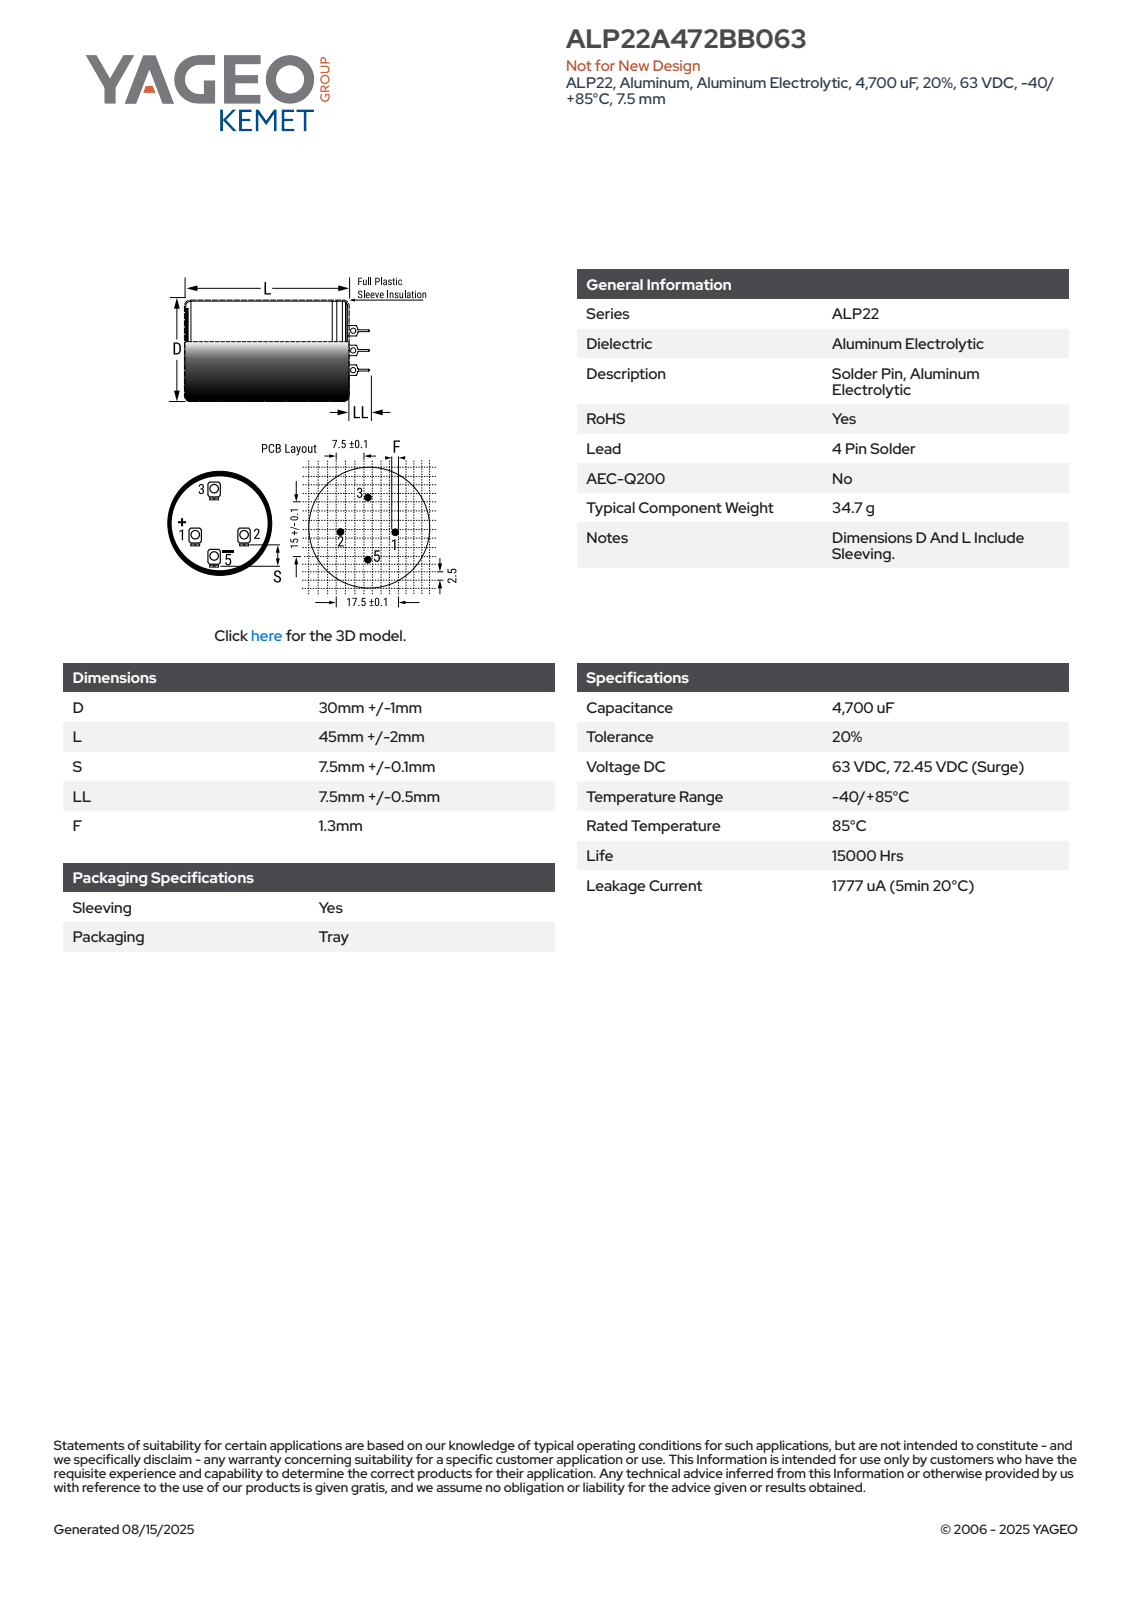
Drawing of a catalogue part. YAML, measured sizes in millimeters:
part_name: "CARS4_D31L47LL7.5S7.5F1.3; Terminal_SolderTag7.5; Terminal_Rivet; Can4_3"
step_written_by: "SolidWorks 2014 (AUTOMOTIVE_DESIGN)"
units: millimeters
bodies: {solids: 9, faces: 230, planar: 113, cylindrical: 59, other: 58}
overall_size: [54.5, 31, 31]
volume: 35253
surface_area: 6376
round_holes:
  - {diameter: 1.3, count: 4}
  - {diameter: 1, count: 3}
round_bosses_or_shafts:
  - {diameter: 3, count: 4}
  - {diameter: 31, count: 1}
partial_cylinders:
  - {radius: 0.32, count: 3}
  - {radius: 15.49, count: 1}
face_to_face_distances: [47, 47.25, 7.5, 10, 17.5, 0.45, 0.7, 47.7, 9.75, 7.75]
hole_center_spacings: [7.5, 10.61, 12.5, 15, 17.5]
